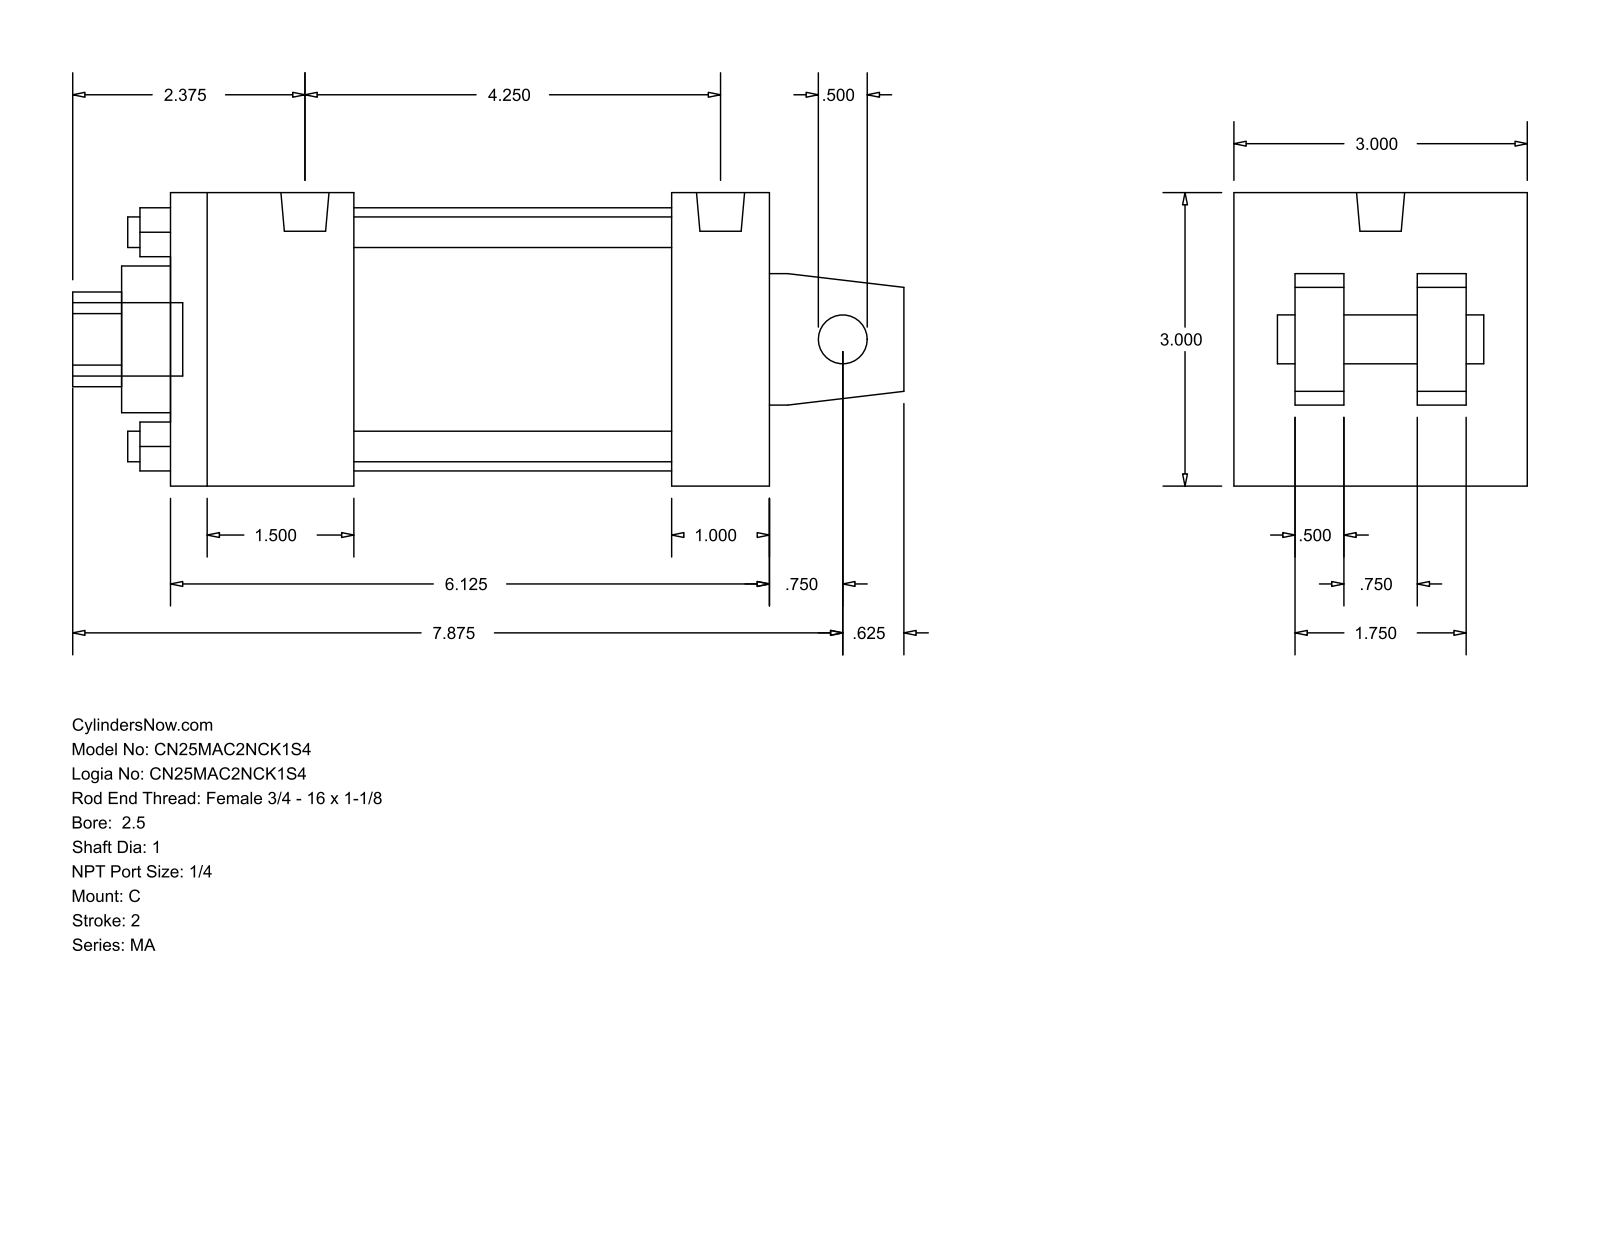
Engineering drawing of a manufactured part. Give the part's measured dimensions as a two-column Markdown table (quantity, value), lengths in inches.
| quantity | value |
| --- | --- |
| part name | MA_C__0250_1 |
| STEP written by | GSSL Pune (CONFIG_CONTROL_DESIGN) |
| units | inches |
| bodies | 0 solids, 103 faces (76 planar, 27 cylindrical, 0 other) |
| overall size | 8.5 × 3 × 3 |
| round holes (diameter × count) | 0.313 × 4, 0.5 × 1, 1 × 1, 1.5 × 1, 2.69 × 1 |
| round bosses / shafts (diameter × count) | 0.313 × 4, 0.492 × 2, 0.75 × 1 |
| partial cylindrical surfaces (radius × count) | 0.484 × 1 |
| main face-to-face distances | 3, 6.125, 1.875, 0.5, 2.375, 0.625, 1, 1.125, 5.125, 3.25 |
| hole center spacings | 1.548, 2.19, 3.097 |
